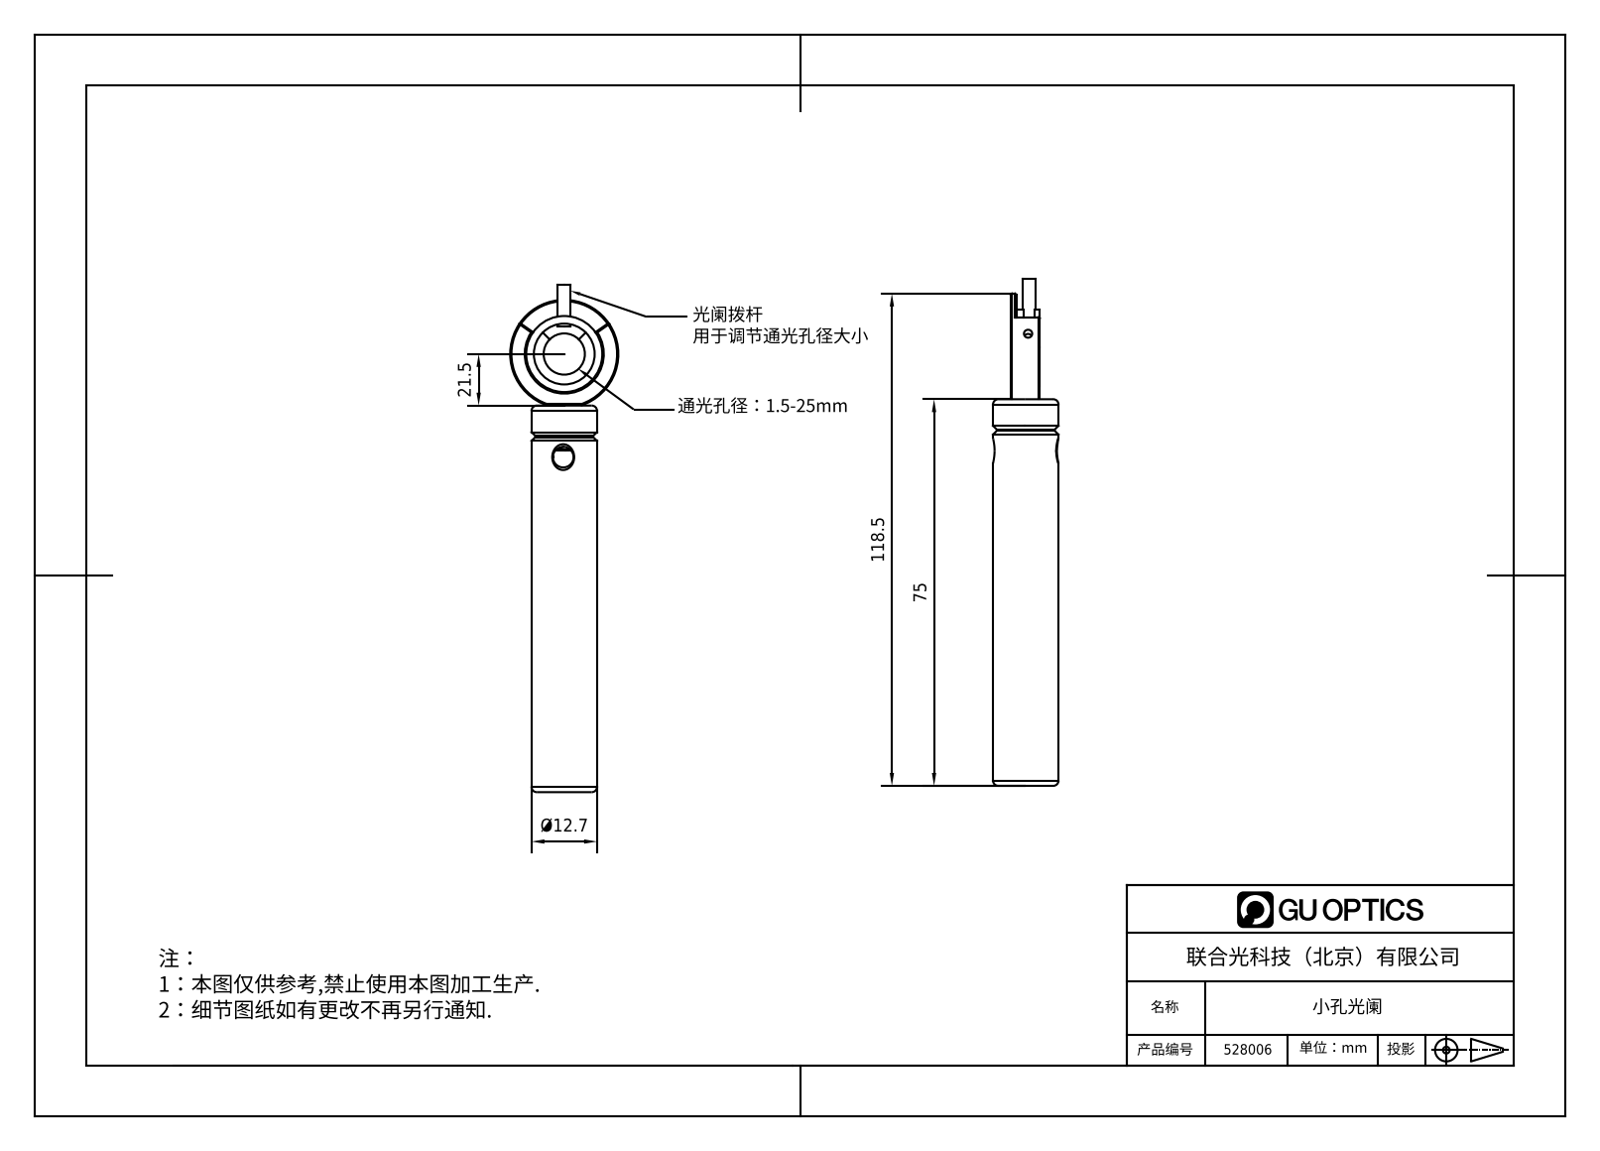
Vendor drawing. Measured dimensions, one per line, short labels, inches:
name: 528006
written by: SolidWorks 2020 (CONFIG_CONTROL_DESIGN)
unit: in
bodies: 6 solids, 95 faces (42 planar, 23 cylindrical, 30 other)
size: 4.665 × 1.732 × 0.5
volume: 0.904 in³; area: 13.99 in²
holes: 2× ⌀0.063, 1× ⌀0.049, 1× ⌀0.13, 1× ⌀0.157, 1× ⌀0.197, 1× ⌀0.984, 1× ⌀1.299, 1× ⌀1.467
bosses: 2× ⌀0.079, 1× ⌀1.732, 1× ⌀1.457, 1× ⌀0.5, 1× ⌀0.157, 1× ⌀0.094, 1× ⌀0.063, 1× ⌀0.055
rounds: 2× R0.03, 1× R0.63
face distances: 0.039, 0.239, 0.199, 0.315, 0.276, 0.076, 0.047, 0.191, 0.268, 0.176
hole spacings: 1.24
